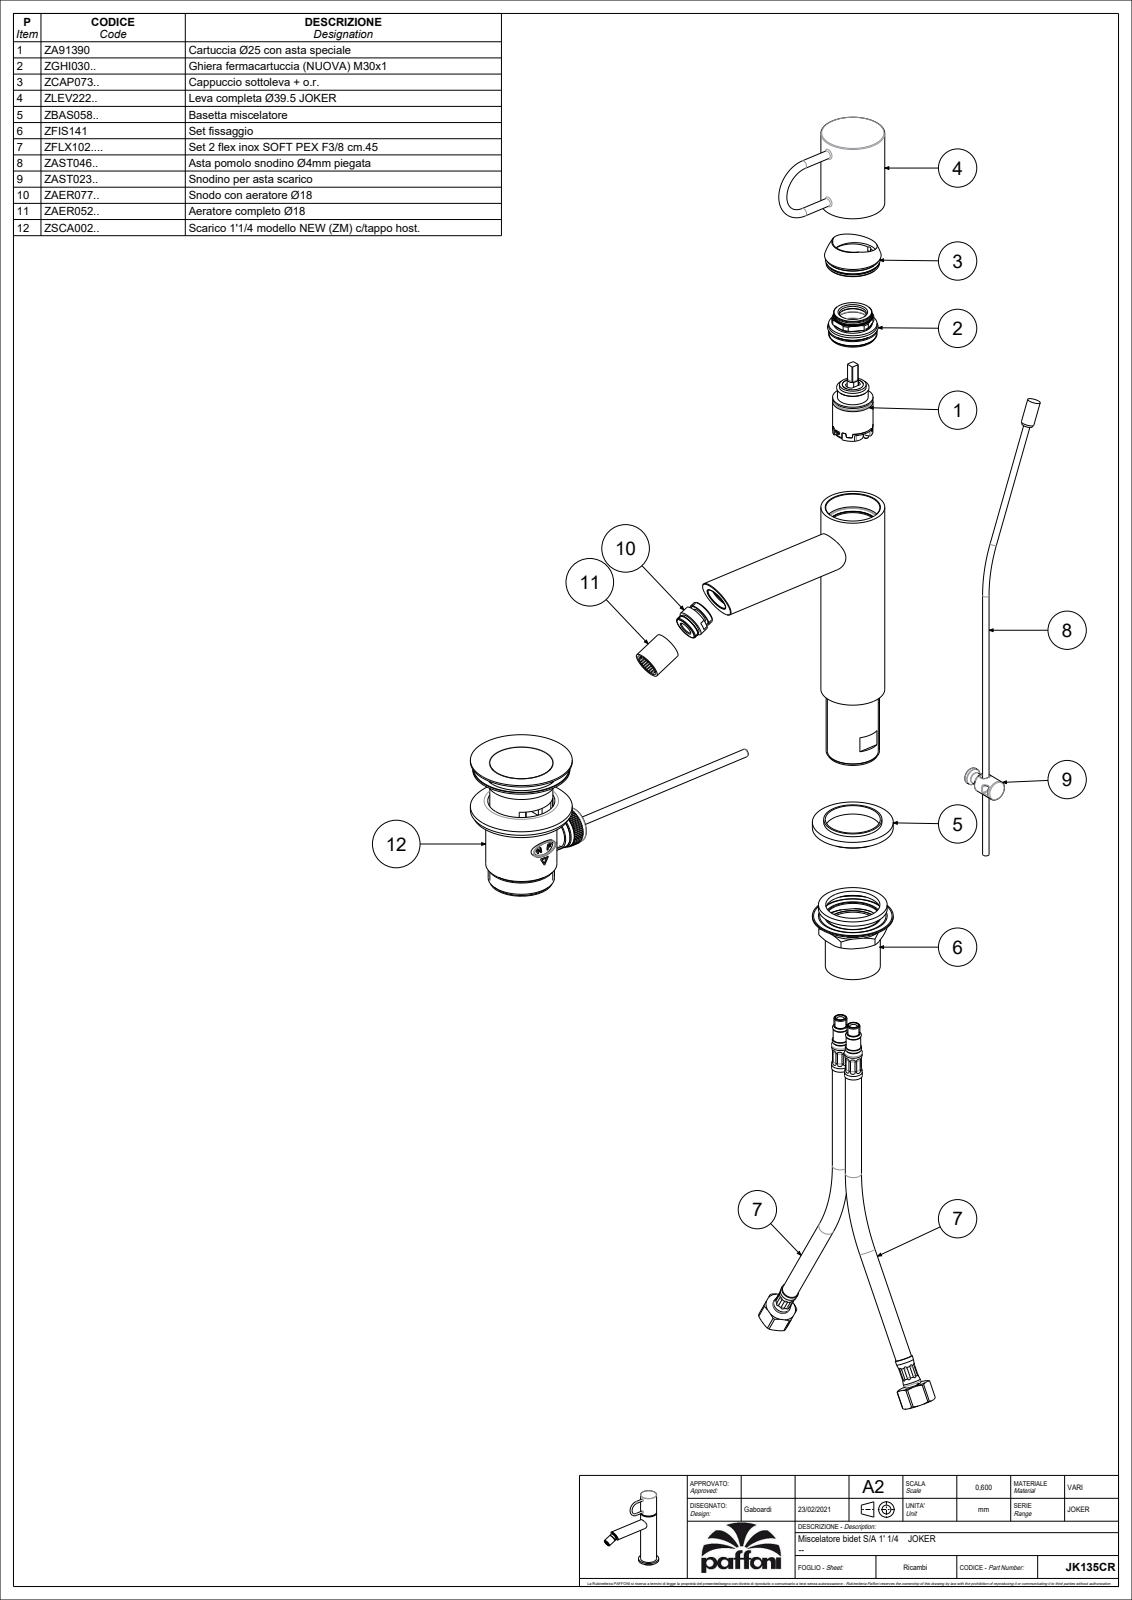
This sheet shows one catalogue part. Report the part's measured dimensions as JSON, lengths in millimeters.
{"part_name": "JK135CR", "step_written_by": "CREO PARAMETRIC BY PTC INC, 2020044 (CONFIG_CONTROL_DESIGN)", "units": "millimeters", "bodies": {"solids": 1, "faces": 55, "planar": 15, "cylindrical": 24, "other": 16}, "overall_size": [186.84, 173.84, 50], "volume_mm3": 281396, "surface_area_mm2": 38830, "round_bosses_or_shafts": [[5, 2], [50, 1], [39.5, 1], [24, 1], [18, 1], [14.5, 1], [10, 1], [8, 1]], "face_to_face_distances": [4, 136.5, 132.5, 2.5, 134, 130, 27, 24.49, 2.51, 18.49]}
